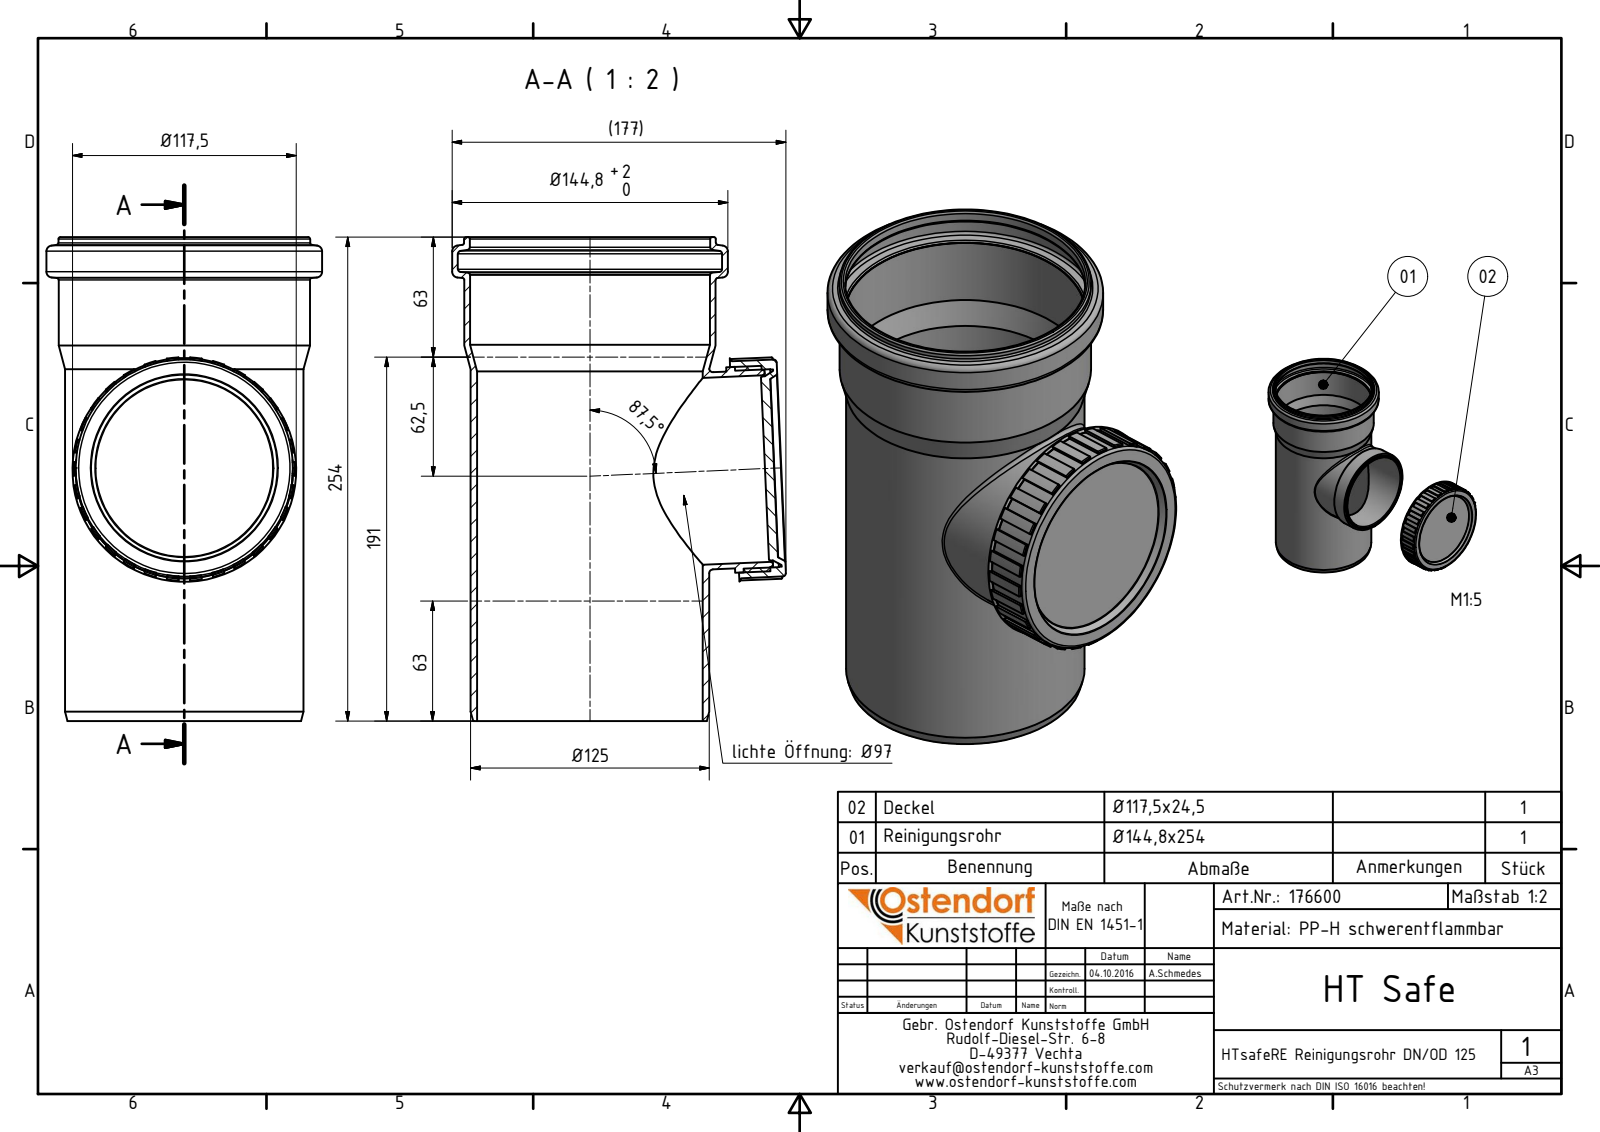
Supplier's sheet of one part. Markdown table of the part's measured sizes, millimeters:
| quantity | value |
| --- | --- |
| part name | 116600 HTRE DN_OD 125; 115600 HTRE DN_OD 110 Deckel; 176600 HTsafeRE DN_OD 125 Zusammenbau |
| STEP written by | Autodesk Inventor 2016 (AUTOMOTIVE_DESIGN) |
| units | millimeters |
| bodies | 2 solids, 266 faces (145 planar, 52 cylindrical, 69 other) |
| overall size | 254 × 175.25 × 144.8 |
| volume | 433 696 mm³ |
| surface area | 263 495 mm² |
| round holes (diameter × count) | 98 × 1, 103.6 × 1, 104 × 1, 108 × 1, 118.5 × 1, 126 × 1, 126.2 × 1, 138.8 × 1 |
| round bosses / shafts (diameter × count) | 103.4 × 2, 144.8 × 1, 132.2 × 1, 132 × 1, 125.3 × 1, 114 × 1, 96.7 × 1 |
| partial cylindrical surfaces (radius × count) | 1 × 4, 58.25 × 1 |
| main face-to-face distances | 2.7, 6.5, 3.8, 18, 20.7, 24.5, 2, 4.54, 16, 4.7 |
